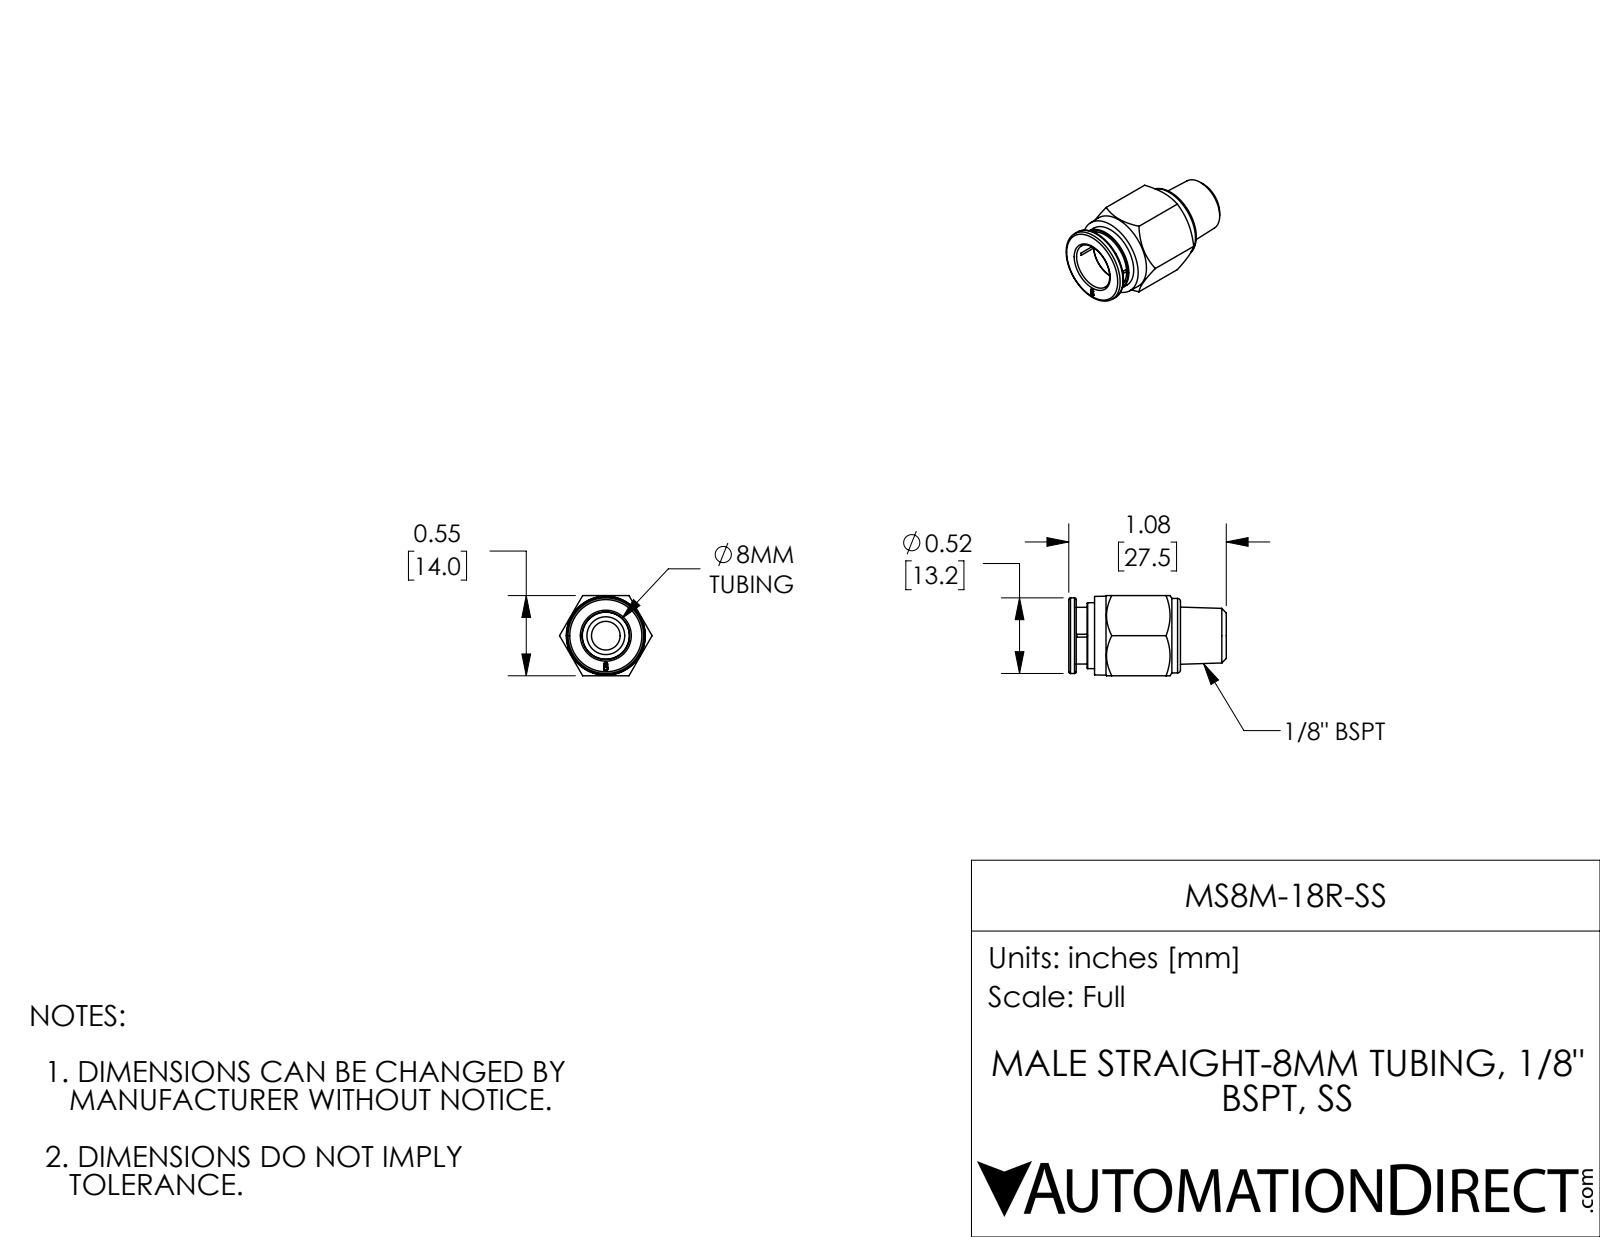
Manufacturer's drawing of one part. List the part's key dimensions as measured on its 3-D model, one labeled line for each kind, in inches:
Part name (STEP PRODUCT): MS8M-18R-SS
STEP written by: SolidWorks 2017 (AUTOMOTIVE_DESIGN)
Units: inches
Bodies: 1 solid, 79 faces (23 planar, 16 cylindrical, 40 other)
Overall size (bounding box): 1.083 × 0.636 × 0.551
Volume: 0.142 in³ · Surface area: 3.302 in²
Round holes (diameter × count): ⌀0.197 ×1, ⌀0.323 ×1, ⌀0.327 ×1, ⌀0.394 ×1
Round bosses / shafts (diameter × count): ⌀0.52 ×1, ⌀0.512 ×1, ⌀0.453 ×1, ⌀0.39 ×1
Main face-to-face distances: 0.551, 0.051, 0.126, 0.177, 0.591, 0.717, 0.768, 0.315, 0.906, 1.031
